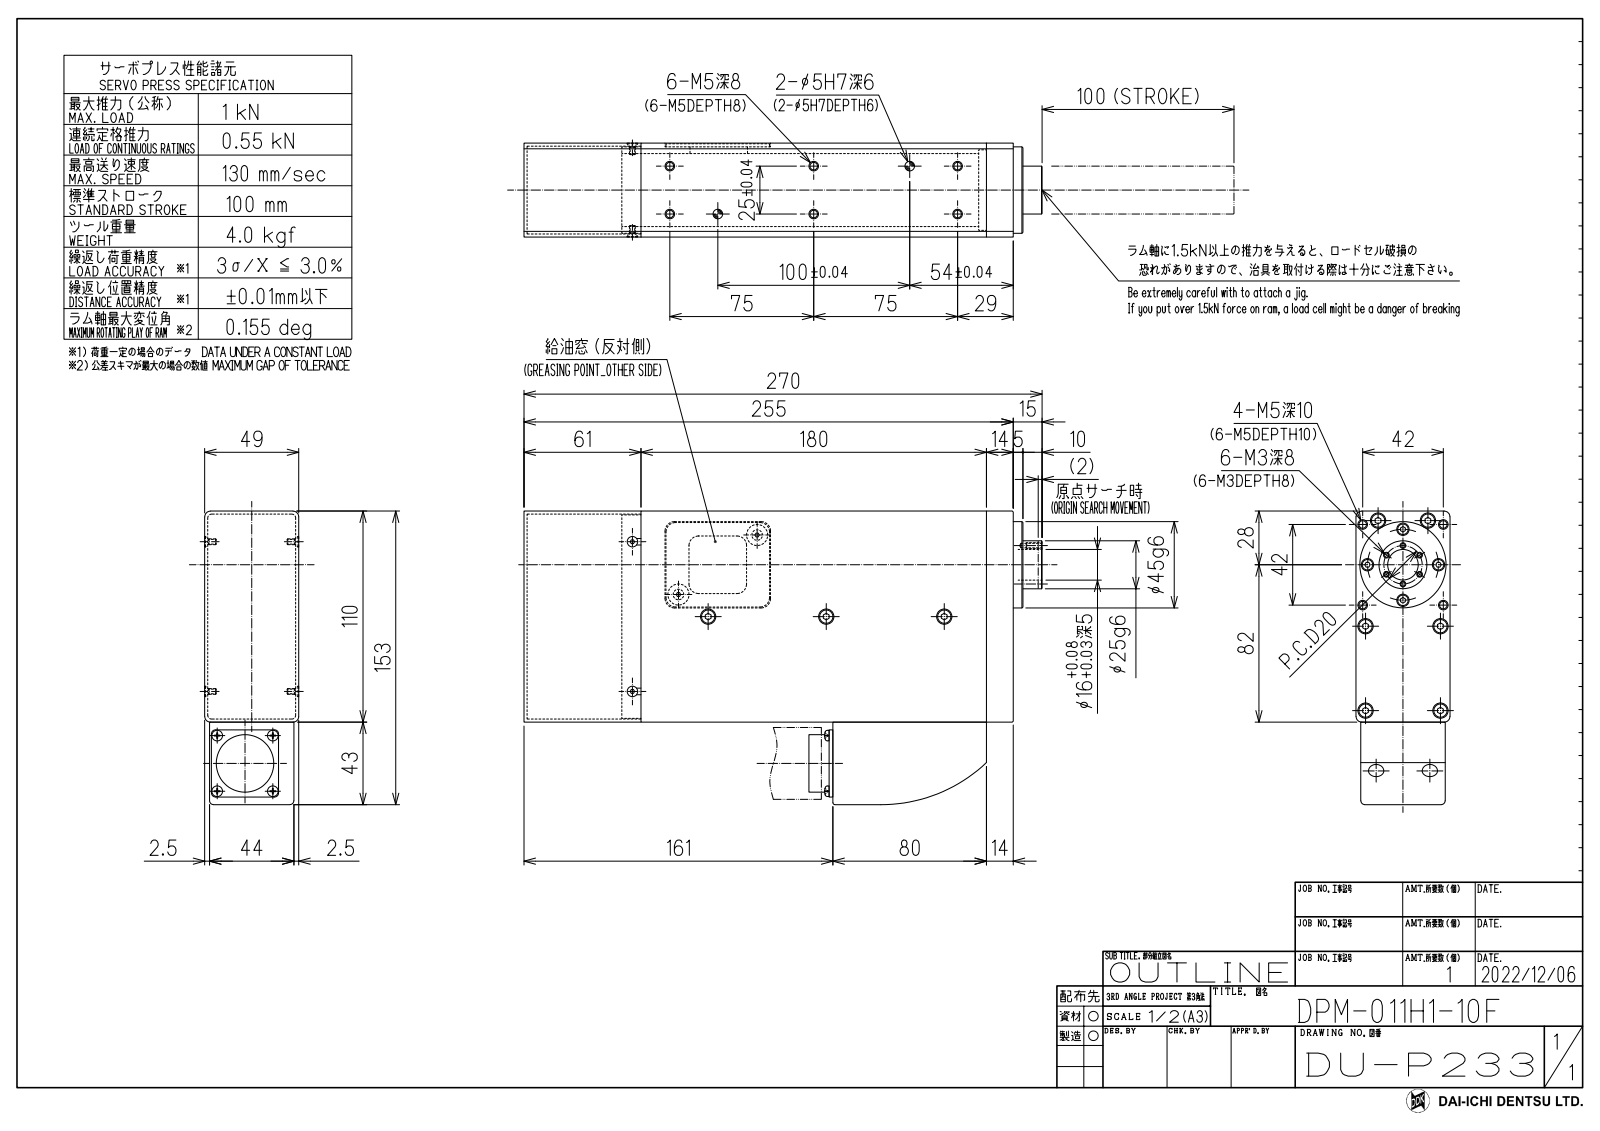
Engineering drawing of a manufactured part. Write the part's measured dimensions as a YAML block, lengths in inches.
part_name: "DPM-011H1-10F(DU-P233+C)_OUTLINE_20221027_Shrinkwrap_1"
step_written_by: "Autodesk Inventor 2023 (CONFIG_CONTROL_DESIGN)"
units: inches
bodies: {solids: 3, faces: 683, planar: 393, cylindrical: 179, other: 111}
overall_size: [10.63, 6.024, 1.929]
volume: 89.77
surface_area: 217.5
round_holes:
  - {diameter: 0.128, count: 16}
  - {diameter: 0.315, count: 13}
  - {diameter: 0.097, count: 11}
  - {diameter: 0.163, count: 10}
  - {diameter: 0.177, count: 7}
  - {diameter: 0.256, count: 5}
  - {diameter: 0.157, count: 4}
  - {diameter: 0.134, count: 3}
  - {diameter: 0.15, count: 2}
  - {diameter: 0.197, count: 2}
  - {diameter: 0.63, count: 1}
  - {diameter: 1.024, count: 1}
round_bosses_or_shafts:
  - {diameter: 0.276, count: 12}
  - {diameter: 0.217, count: 12}
  - {diameter: 0.106, count: 4}
  - {diameter: 0.157, count: 3}
  - {diameter: 0.118, count: 2}
  - {diameter: 1.772, count: 1}
  - {diameter: 1.26, count: 1}
  - {diameter: 1.181, count: 1}
partial_cylinders:
  - {radius: 0.197, count: 18}
  - {radius: 0.079, count: 11}
  - {radius: 0.118, count: 4}
  - {radius: 0.142, count: 4}
  - {radius: 0.157, count: 3}
  - {radius: 0.827, count: 2}
  - {radius: 0.048, count: 1}
  - {radius: 3.15, count: 1}
face_to_face_distances: [1.929, 4.331, 0.098, 1.831, 0.472, 1.26, 0.571, 1.358, 0.079, 0.236]
hole_center_spacings: [0.394, 0.557, 0.728, 0.833, 1.03, 1.346, 1.378, 1.761]
